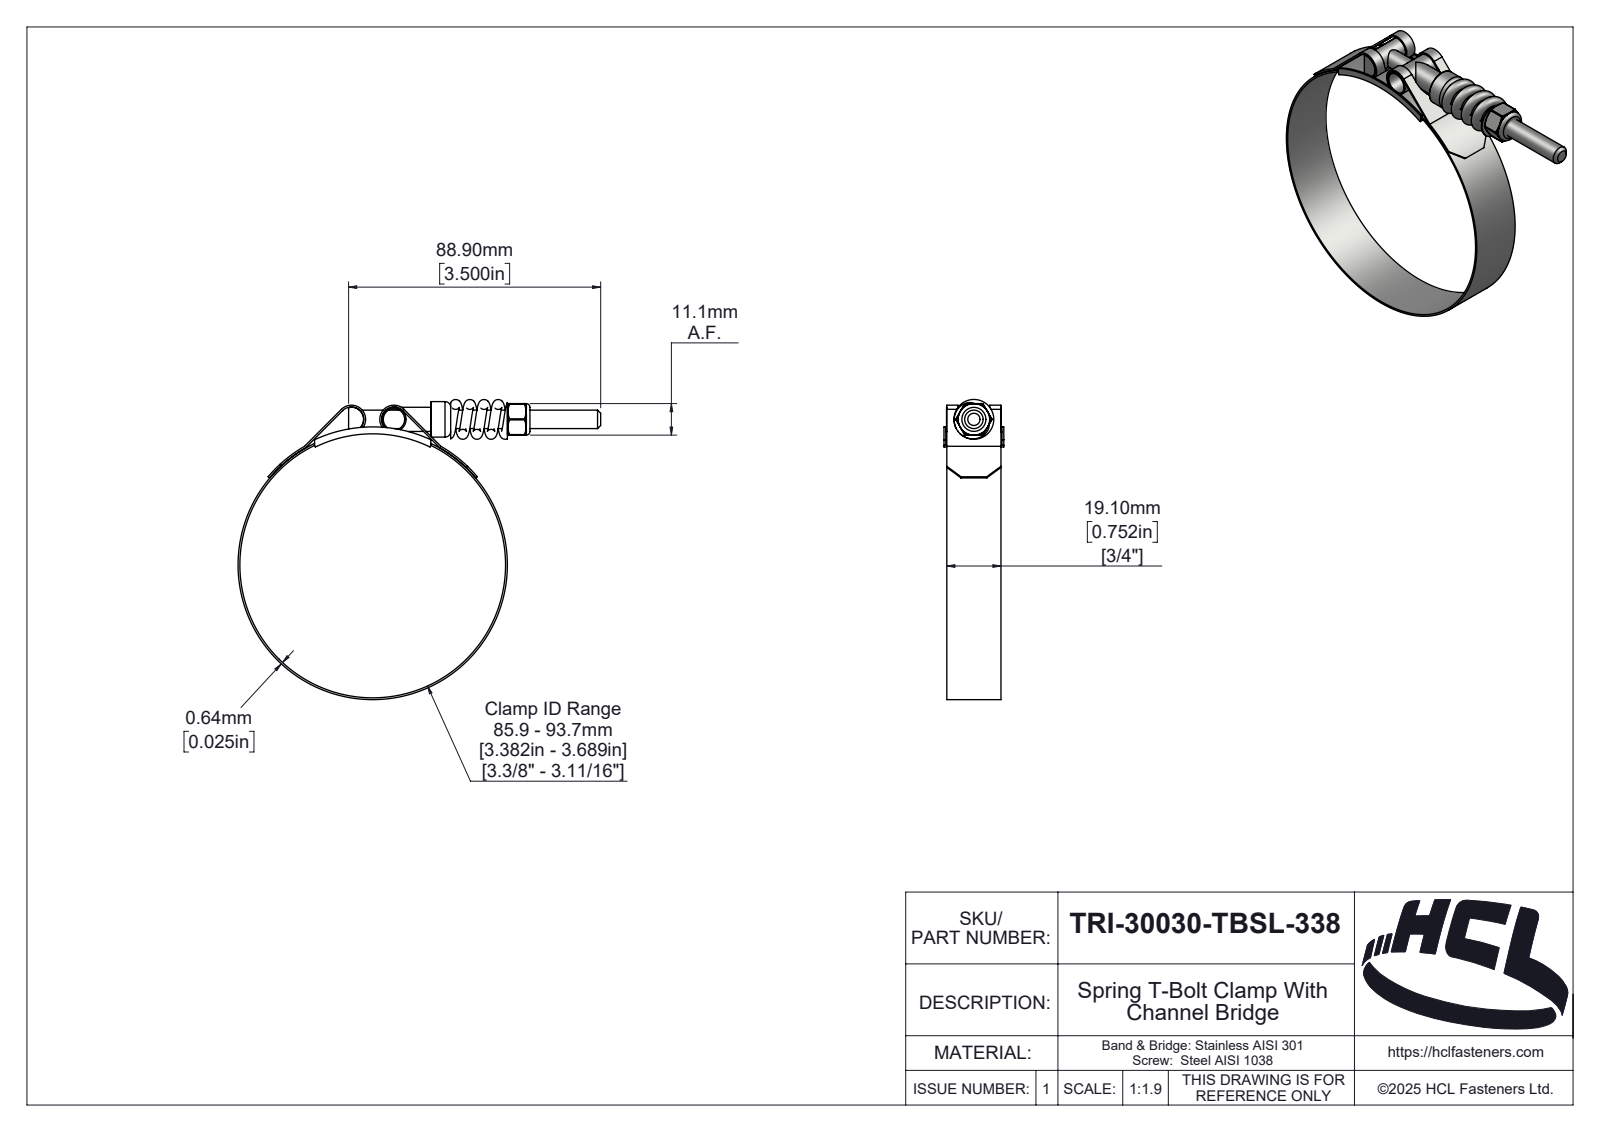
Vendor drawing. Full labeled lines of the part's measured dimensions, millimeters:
Part name (STEP PRODUCT): TRI-30030-TBSL-338
STEP written by: SolidWorks 2025 (AUTOMOTIVE_DESIGN)
Units: millimetres
Bodies: 7 solids, 332 faces (48 planar, 122 cylindrical, 162 other)
Overall size (bounding box): 128.89 × 105.82 × 21.1
Volume: 11 487 mm³ · Surface area: 23 038 mm²
Round holes (diameter × count): ⌀5.4 ×1, ⌀6.35 ×1, ⌀6.5 ×1, ⌀7.52 ×1, ⌀93.7 ×1
Round bosses / shafts (diameter × count): ⌀8.52 ×2, ⌀94.98 ×1, ⌀12.52 ×1
Partial cylindrical surfaces — rounded edges, fillets, slot ends (radius × count): R0.39 ×6, R0.5 ×2, R4.36 ×2, R5 ×2, R0.59 ×1, R2.42 ×1, R3.03 ×1, R3.19 ×1
Main face-to-face distances: 0.64, 19.1, 1, 20.1, 20.46, 0.36, 19.46, 56, 11.11, 21.1
Hole centre spacings: 51.85
